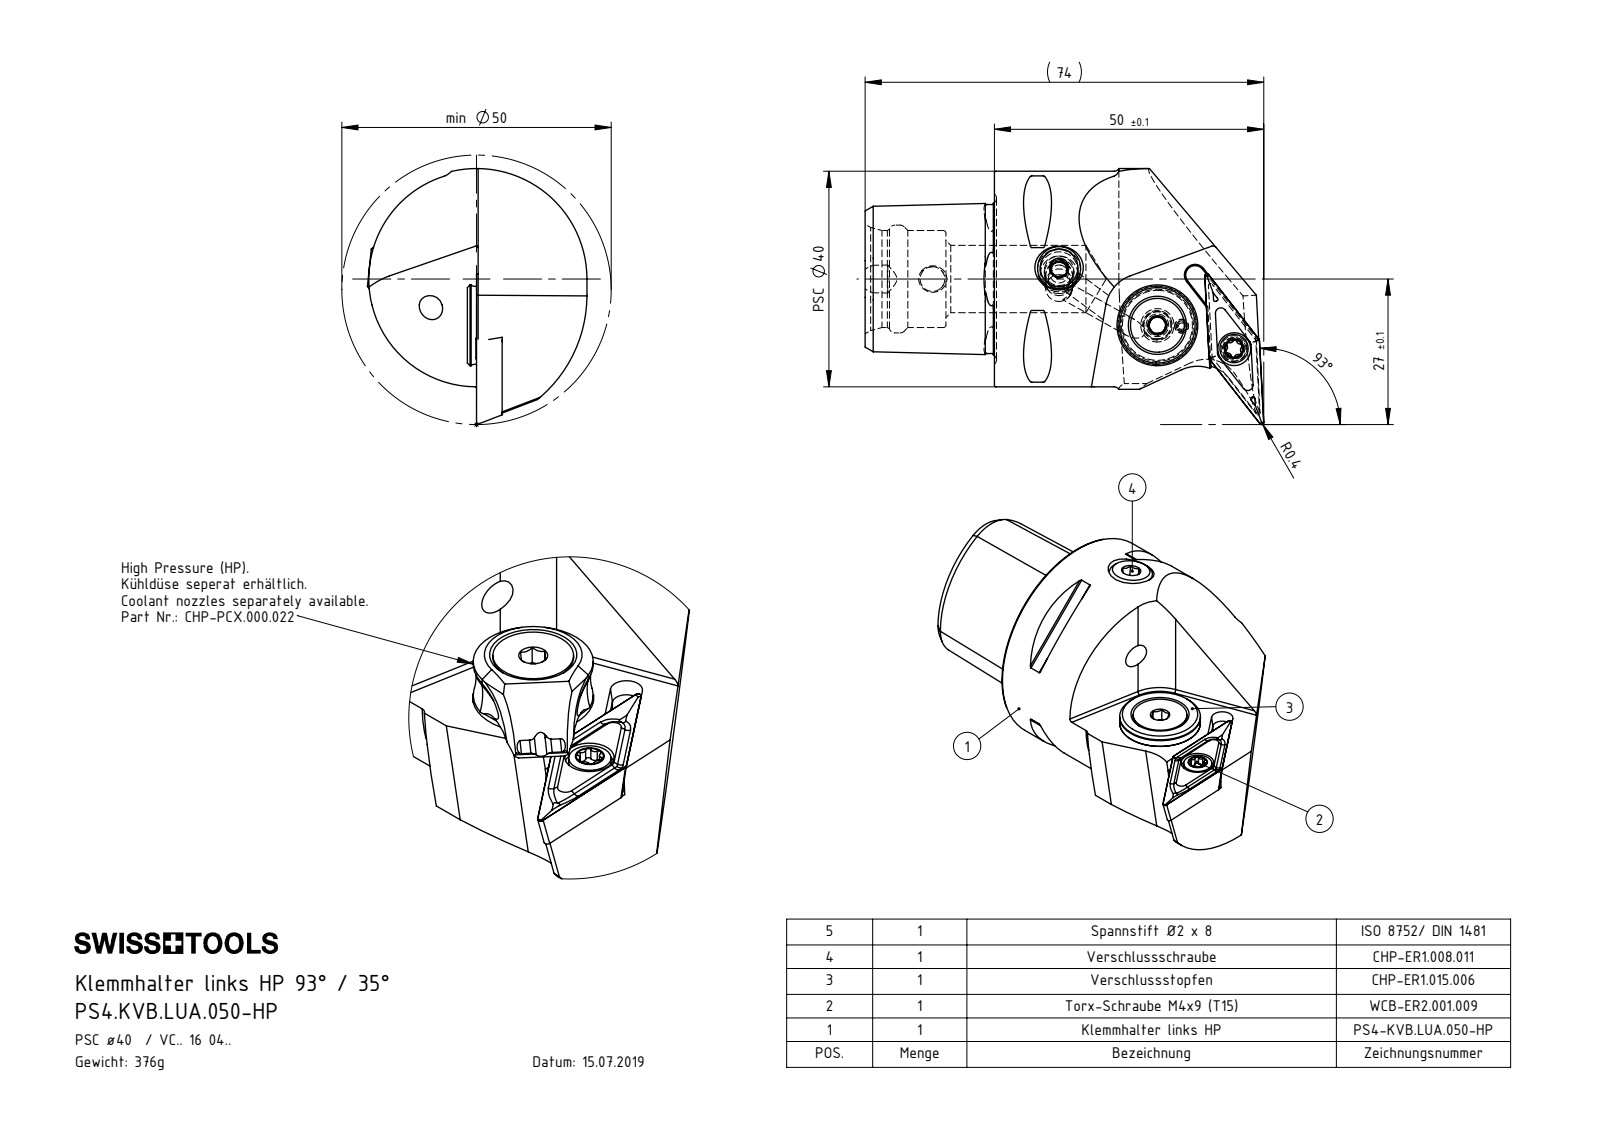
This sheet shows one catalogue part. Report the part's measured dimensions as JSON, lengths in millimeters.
{"part_name": "PS4.KVB.LUA.050-HP; PS4-KVB.LUA.050-HP_A_Fertigbearbeitung; CHP-ER1.015.006; DIN 7991 - M5x15 (+6 more)", "step_written_by": "SolidWorks 2017 (AUTOMOTIVE_DESIGN)", "units": "millimeters", "bodies": {"solids": 8, "faces": 284, "planar": 94, "cylindrical": 62, "other": 128}, "overall_size": [74, 47.5, 40.76], "volume_mm3": 47841, "surface_area_mm2": 15365, "round_holes": [[3.3, 2], [4.2, 2], [1.2, 1], [2, 1], [2.5, 1], [3, 1], [4, 1], [4.4, 1], [4.6, 1], [5, 1], [5.2, 1], [6.1, 1]], "round_bosses_or_shafts": [[40, 1], [15, 1], [13.4, 1], [10, 1], [8, 1], [5.5, 1], [5.25, 1], [5, 1]], "partial_cylinders_radius": [[0.3, 8], [0.34, 6], [0.59, 6], [0.5, 2], [7, 2], [1.75, 1], [3, 1], [20.5, 1]], "face_to_face_distances": [4.5, 4.46, 24, 15.52, 35.3, 15, 6.4, 6.36, 1.9, 9], "hole_center_spacings": [4.5, 10.58, 10.66, 14.87, 14.94, 20.17, 23.5, 24.37]}
